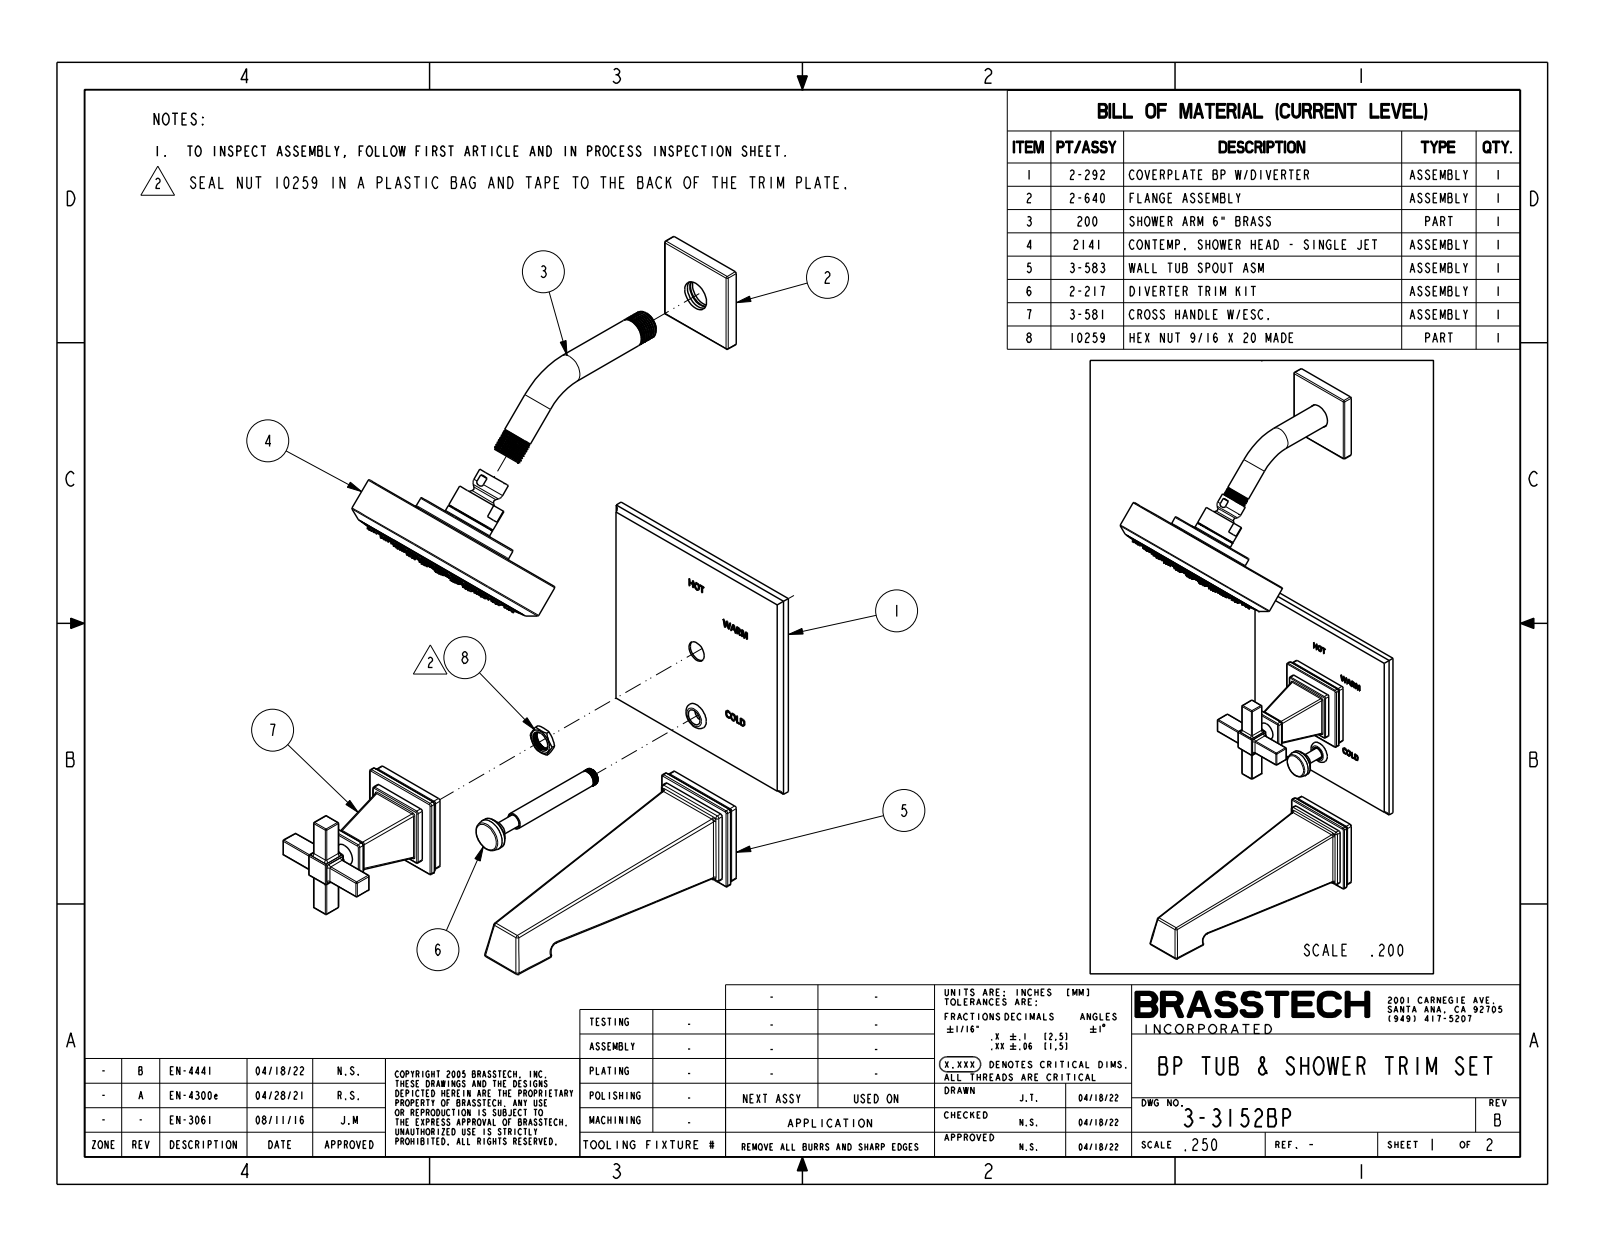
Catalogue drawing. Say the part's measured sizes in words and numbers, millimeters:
The part is named "3-3152BP". Its 3-D file was written by "CREO PARAMETRIC BY PTC INC, 2018400 (CONFIG_CONTROL_DESIGN)". It is 3 solids with 1492 faces: 302 planar, 387 cylindrical and 803 other. Overall it measures 520.7 by 215.5 by 165.1 millimeters. Its volume is 1 291 000 cubic millimeters and its surface area 191 700 square millimeters. Round holes: 90 of diameter 1.3, 1 of diameter 5.6, 1 of diameter 133.5. Round bosses or shafts: 2 of diameter 35.6, 2 of diameter 20.7, 1 of diameter 150.1, 1 of diameter 132.6, 1 of diameter 74.2, 1 of diameter 23, 1 of diameter 22.9, 1 of diameter 19.5. Partial cylindrical surfaces (rounded edges, fillets, slot ends): 68 of radius 0.8, 57 of radius 1.5, 12 of radius 2.3, 8 of radius 1, 4 of radius 3.2, 4 of radius 5.8, 4 of radius 8.1, 1 of radius 5.1. The main face-to-face distances are 8, 10.4, 8.9, 0.9, 7.4, 2.5, 1.5, 76.2, 88.9, 12.7. The hole center spacings are 24.9, 35.8, 10.9, 14, 34.1, 48.1, 14.6, 21.6.
